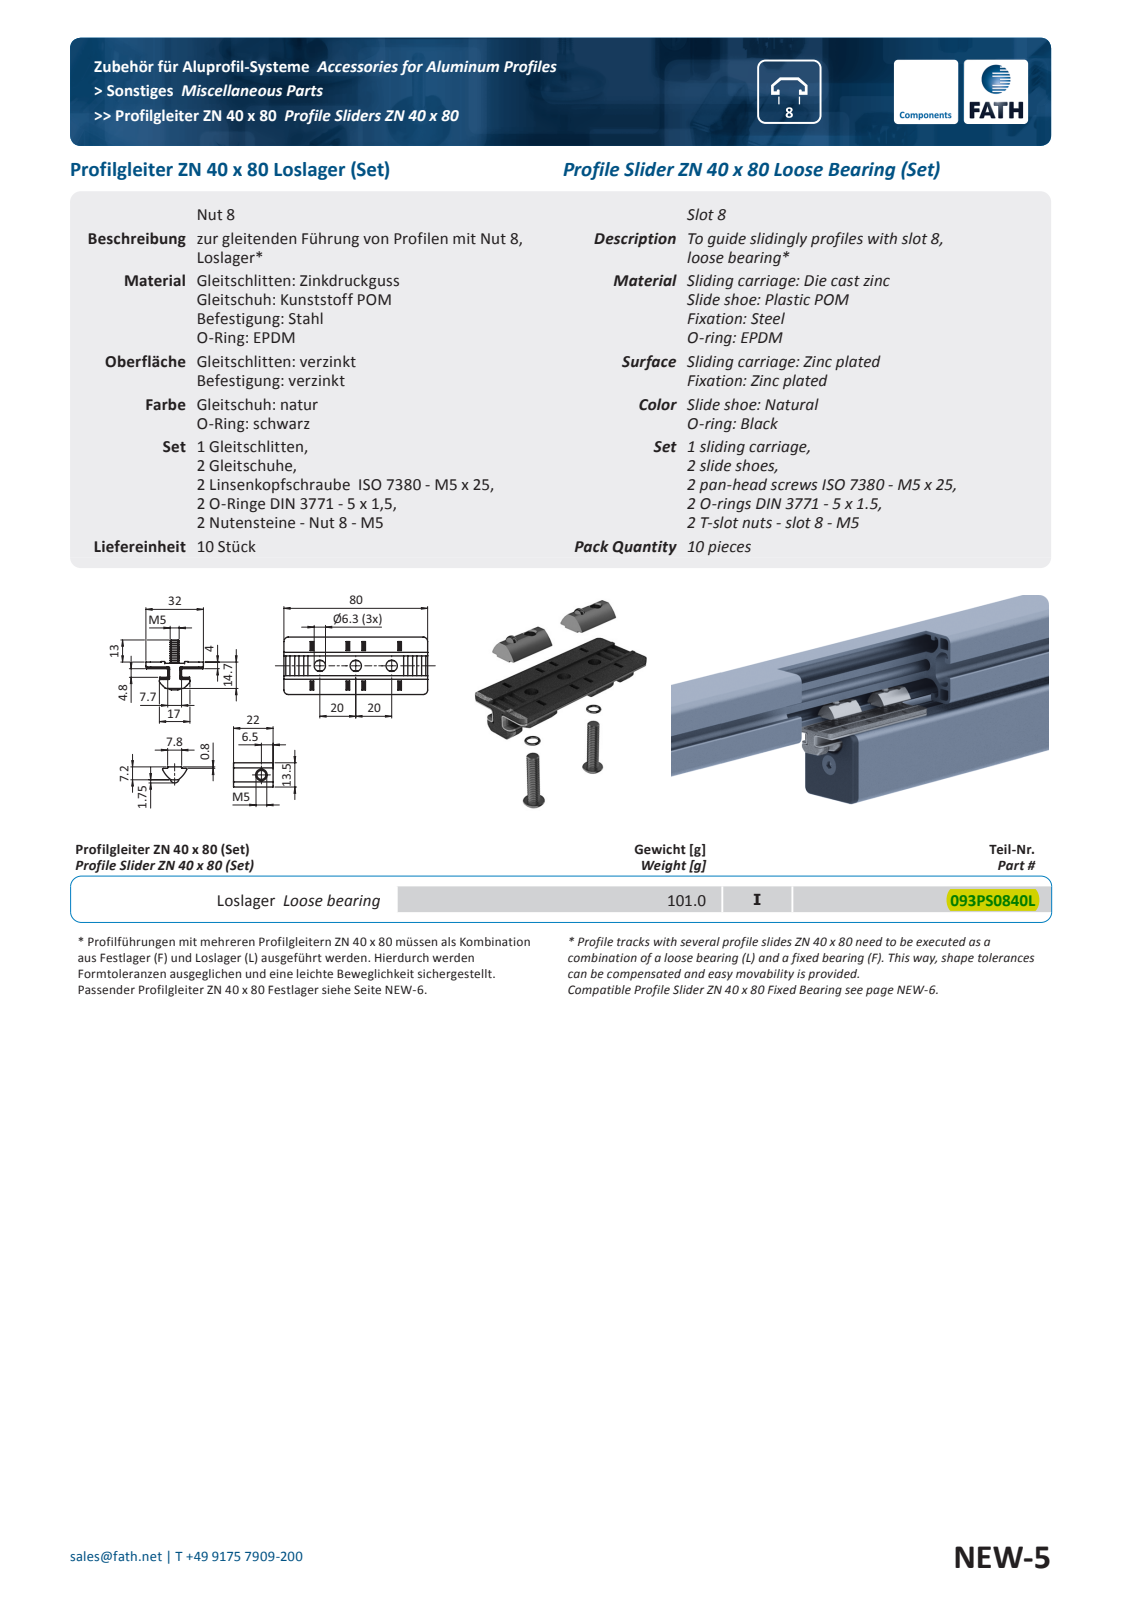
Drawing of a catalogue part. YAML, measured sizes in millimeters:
part_name: "fath_093ps0840l_1; fath_093ps0840l_2; fath_093ps0840l_3; fath_093ps0840l_4 (+5 more)"
step_written_by: "Spatial InterOp 3D (automotive_design)"
units: millimeters
bodies: {solids: 9, faces: 661, planar: 259, cylindrical: 258, other: 144}
overall_size: [80, 32, 27.8]
volume: 17874
surface_area: 19639
round_holes:
  - {diameter: 6.3, count: 3}
  - {diameter: 4.2, count: 2}
  - {diameter: 5, count: 2}
round_bosses_or_shafts:
  - {diameter: 5, count: 2}
partial_cylinders:
  - {radius: 0.5, count: 50}
  - {radius: 1, count: 38}
  - {radius: 0.3, count: 28}
  - {radius: 2.5, count: 24}
  - {radius: 0.1, count: 6}
  - {radius: 0.2, count: 4}
  - {radius: 1.5, count: 4}
  - {radius: 2, count: 4}
face_to_face_distances: [1, 2.7, 3.7, 3, 5.8, 8.8, 2, 5.7, 8.5, 0.7]
hole_center_spacings: [9.5, 10.5, 20, 30.5, 21, 40]
